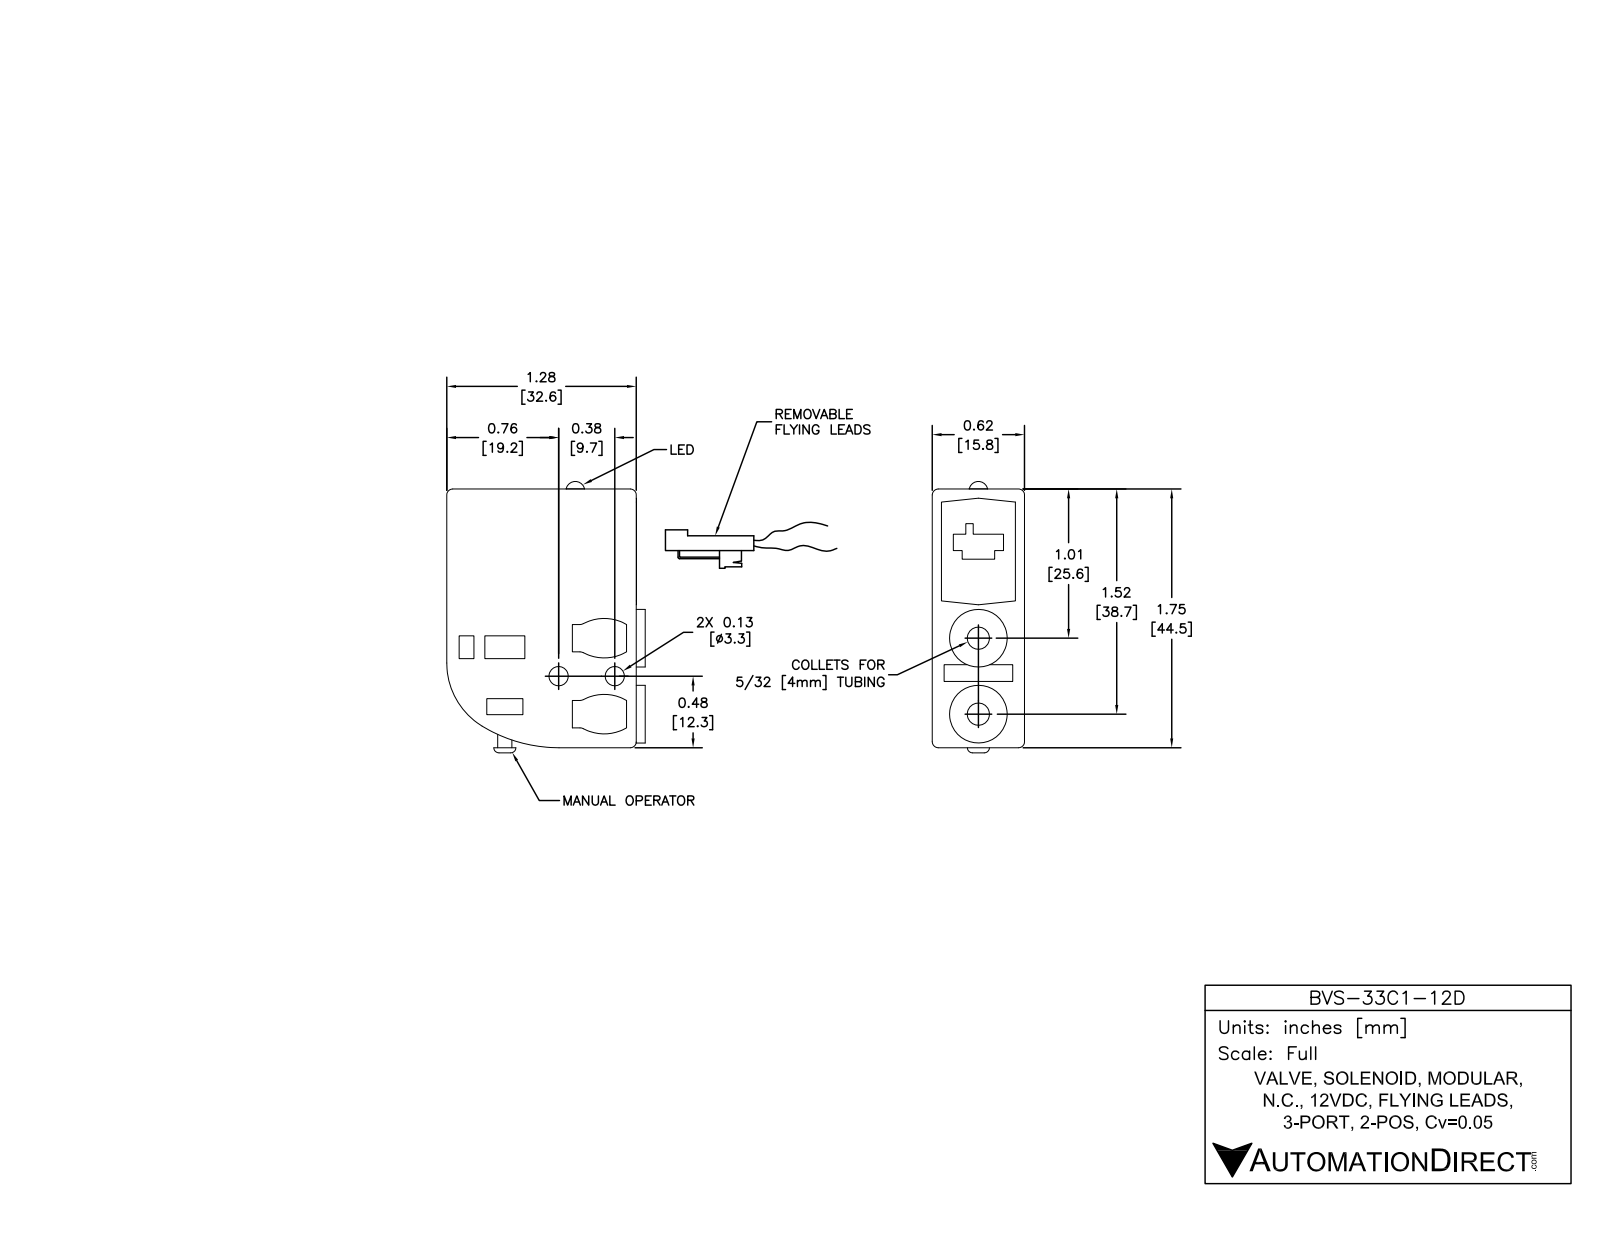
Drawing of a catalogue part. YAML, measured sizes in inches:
part_name: "BVS-33C1-12D"
step_written_by: "SolidWorks 2013 (AUTOMOTIVE_DESIGN)"
units: inches
bodies: {solids: 1, faces: 158, planar: 93, cylindrical: 52, other: 13}
overall_size: [1.836, 1.347, 0.624]
volume: 1.246
surface_area: 10.17
round_holes:
  - {diameter: 0.13, count: 2}
  - {diameter: 0.15, count: 2}
  - {diameter: 0.254, count: 2}
  - {diameter: 0.046, count: 1}
round_bosses_or_shafts:
  - {diameter: 0.39, count: 2}
  - {diameter: 0.124, count: 1}
  - {diameter: 0.096, count: 1}
partial_cylinders:
  - {radius: 0.04, count: 11}
  - {radius: 0.05, count: 4}
  - {radius: 0.3, count: 4}
  - {radius: 0.5, count: 1}
  - {radius: 1, count: 1}
face_to_face_distances: [0.624, 0.1, 0.524, 1.287, 1.288, 1.75, 0.424, 0.06, 0.059, 1.347]
hole_center_spacings: [0.061, 0.38, 0.453, 0.514]
